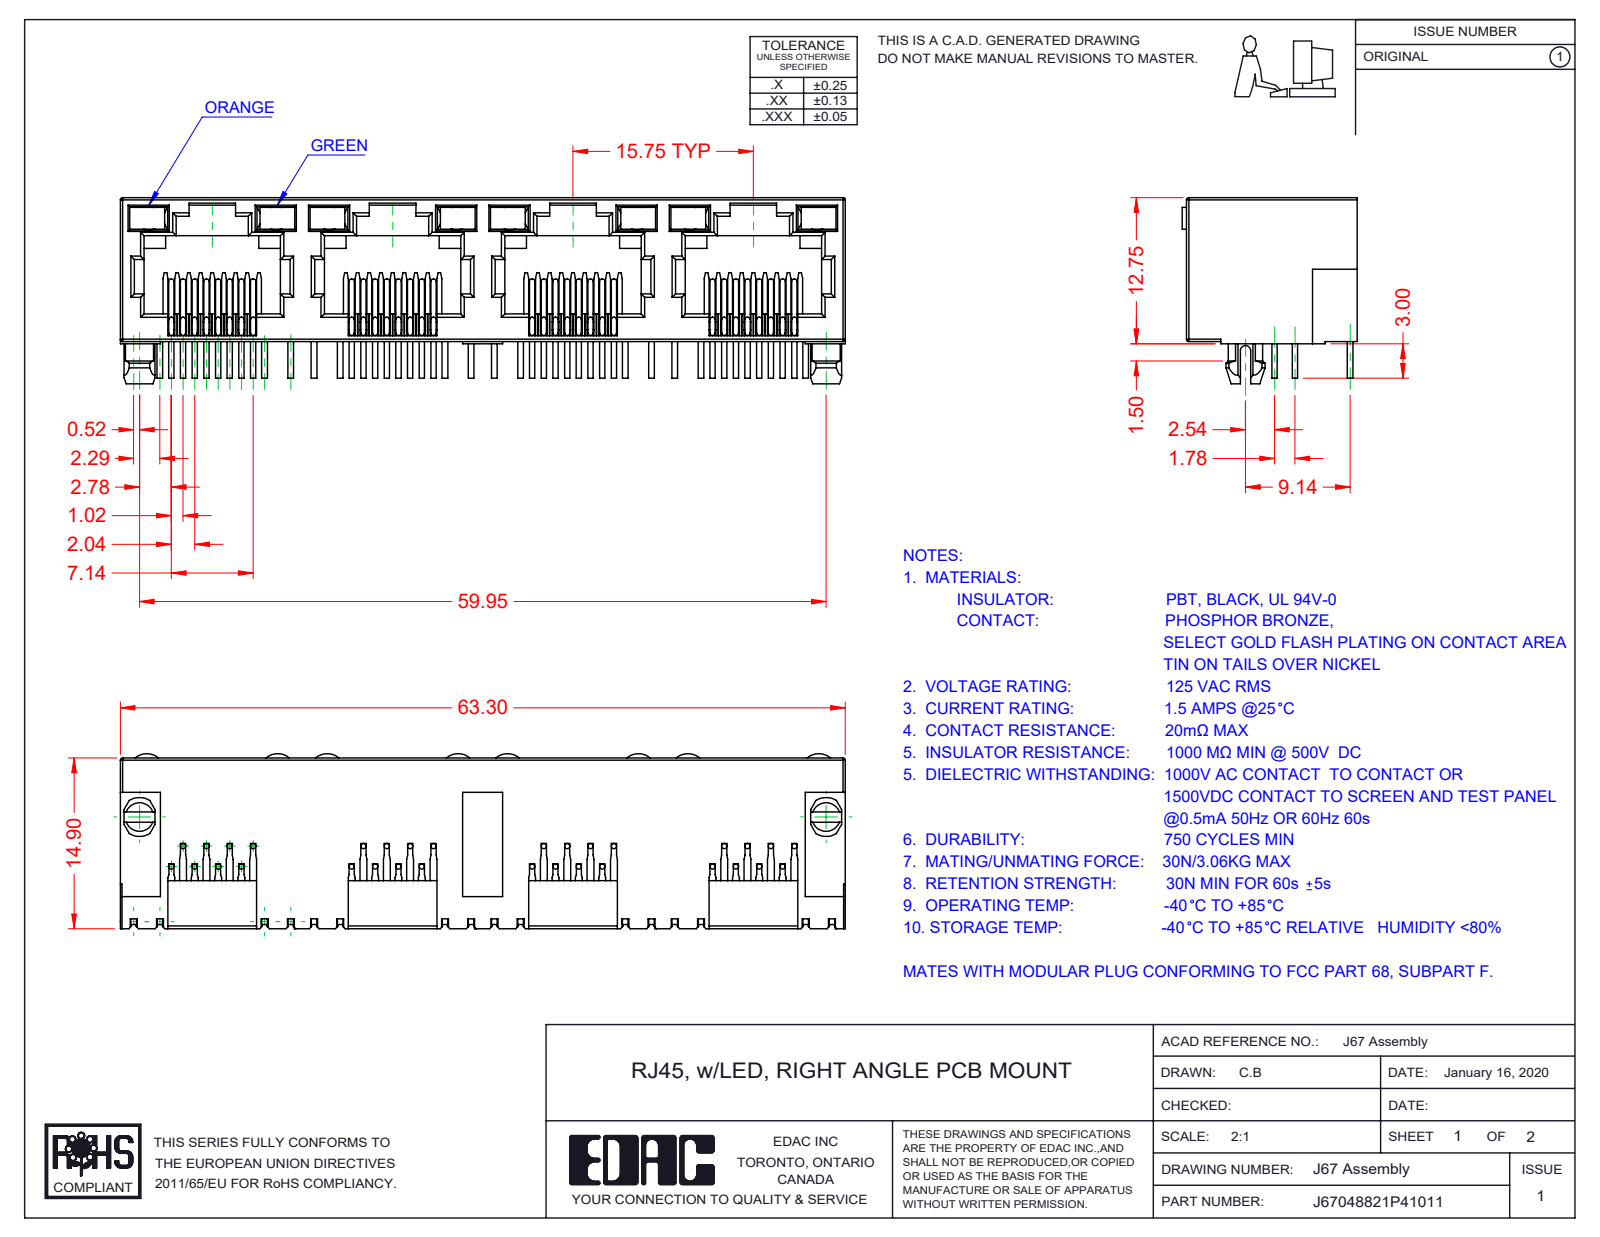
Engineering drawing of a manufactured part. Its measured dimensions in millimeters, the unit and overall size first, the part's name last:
Units: millimetres
Overall size (bounding box): 63.3 × 16.25 × 15.28
Round bosses / shafts (diameter × count): ⌀0.46 ×96
Partial cylindrical surfaces — rounded edges, fillets, slot ends (radius × count): R0.2 ×66, R0.3 ×29, R0.45 ×9, R1.55 ×8, R1.5 ×2, R1.7 ×2, R0.35 ×1, R1 ×1
Main face-to-face distances: 0.5, 12.55, 1.89, 0.89, 10, 15.75, 1, 1.39, 11, 11.89
Volume: 5 159 mm³ · Surface area: 11 573 mm²
Bodies: 41 solids, 2465 faces (1781 planar, 476 cylindrical, 208 other)
Part name (STEP PRODUCT): 67 LED LH_4-Orange; J67048822P43011; 67 LED RH_3-Green; 67 Insulator (+1 more)
STEP written by: SolidWorks 2016 (CONFIG_CONTROL_DESIGN)
